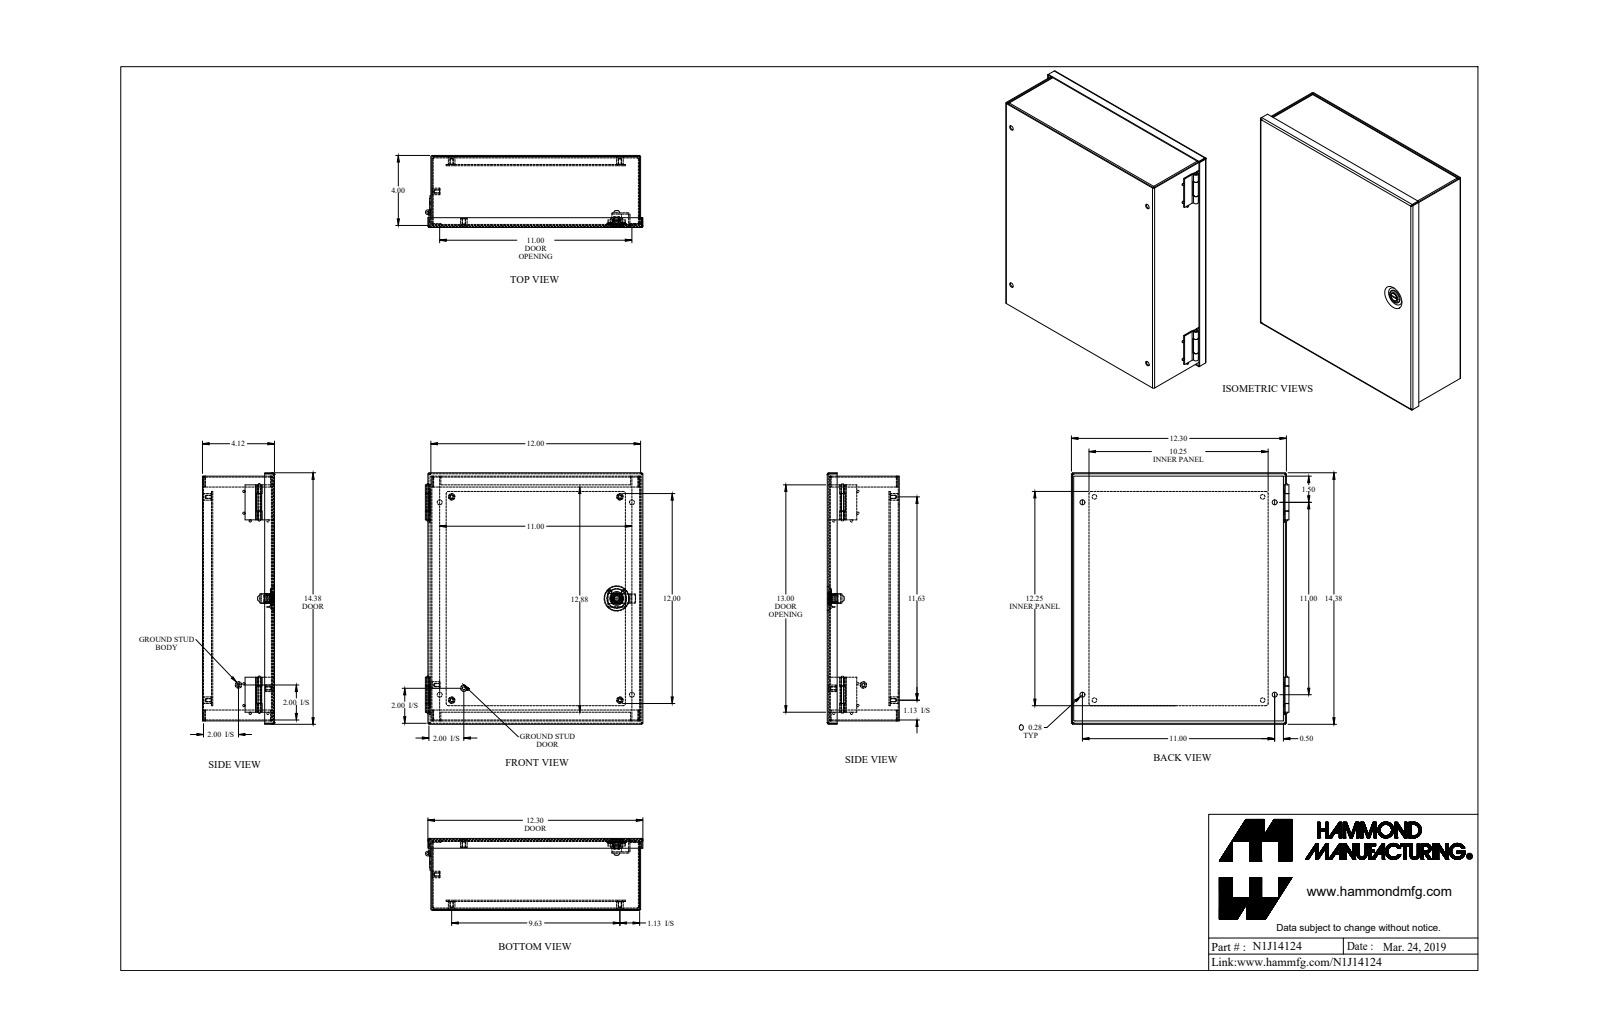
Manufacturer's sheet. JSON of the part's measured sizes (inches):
{"part_name": "N1J14124", "step_written_by": "SolidWorks 2018 (AUTOMOTIVE_DESIGN)", "units": "inches", "bodies": {"solids": 18, "faces": 477, "planar": 224, "cylindrical": 188, "other": 65}, "overall_size": [14.38, 12.443, 4.118], "volume_in3": 45.24, "surface_area_in2": 1527, "round_holes": [[0.156, 6], [0.265, 4], [0.28, 4], [0.125, 1], [0.319, 1], [0.476, 1]], "round_bosses_or_shafts": [[0.131, 8], [0.375, 6], [0.787, 1], [0.547, 1], [0.472, 1], [0.469, 1], [0.366, 1], [0.32, 1]], "partial_cylinders_radius": [[0.029, 16], [0.086, 16], [0.012, 4], [0.1, 4], [0.125, 4], [0.036, 2], [0.079, 2], [0.25, 2]], "face_to_face_distances": [0.057, 4.061, 4.004, 4.118, 0.072, 0.517, 0.46, 3.544, 3.601, 0.589], "hole_center_spacings": [0.755, 10.317, 11, 11.333, 15.307, 5.569, 5.815, 9.625]}
